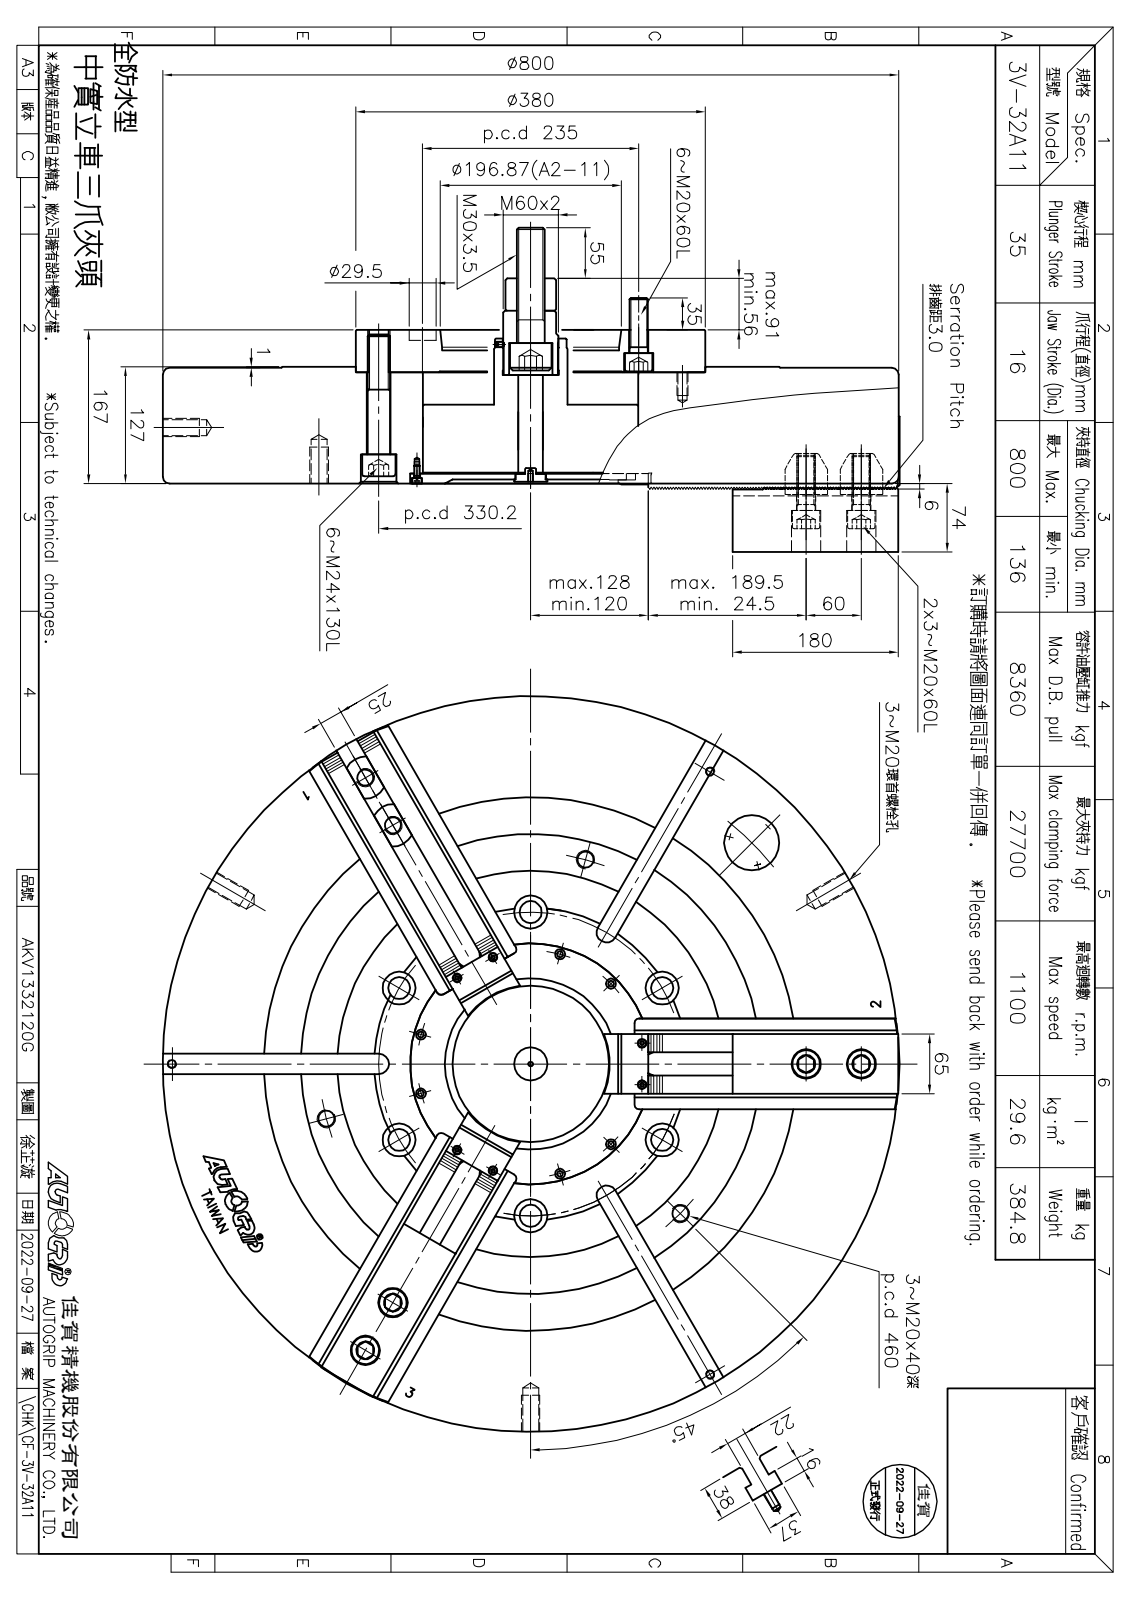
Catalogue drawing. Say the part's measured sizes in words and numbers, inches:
The part is named "圓頭內六角螺栓_M30x125(全牙); CF-3P-15-06000; CF-3P-15-05000; CF-3H-221-04000(T型塊) (+8 more)". Its 3-D file was written by "SolidWorks 2016 (CONFIG_CONTROL_DESIGN)". It is 47 solids with 6424 faces: 4847 planar, 1211 cylindrical and 366 other. Overall it measures 31.535 by 31.496 by 13.866 inches. Its volume is 4 114 cubic inches and its surface area 4 878 square inches. Round holes: 18 of diameter 0.827, 12 of diameter 0.689, 12 of diameter 1.26, 9 of diameter 0.433, 7 of diameter 0.197, 6 of diameter 0.26, 6 of diameter 0.866, 6 of diameter 1.024, 6 of diameter 1.535, 3 of diameter 0.335, 3 of diameter 0.402, 3 of diameter 1.161. Round bosses or shafts: 12 of diameter 1.181, 12 of diameter 0.787, 7 of diameter 1.417, 6 of diameter 0.945, 6 of diameter 0.394, 6 of diameter 0.236, 1 of diameter 31.496, 1 of diameter 3.071. Partial cylindrical surfaces (rounded edges, fillets, slot ends): 423 of radius 0.004, 6 of radius 0.906, 3 of radius 0.433, 3 of radius 0.492, 3 of radius 0.728, 3 of radius 15.748, 1 of radius 4.409, 1 of radius 5.157. The main face-to-face distances are 4.961, 2.559, 0.039, 0.197, 4.764, 0.236, 1.575, 5, 4.528, 1.614. The hole center spacings are 6.5, 1.697, 4.975, 7.038, 7.914, 10.313, 12.01, 12.889.
